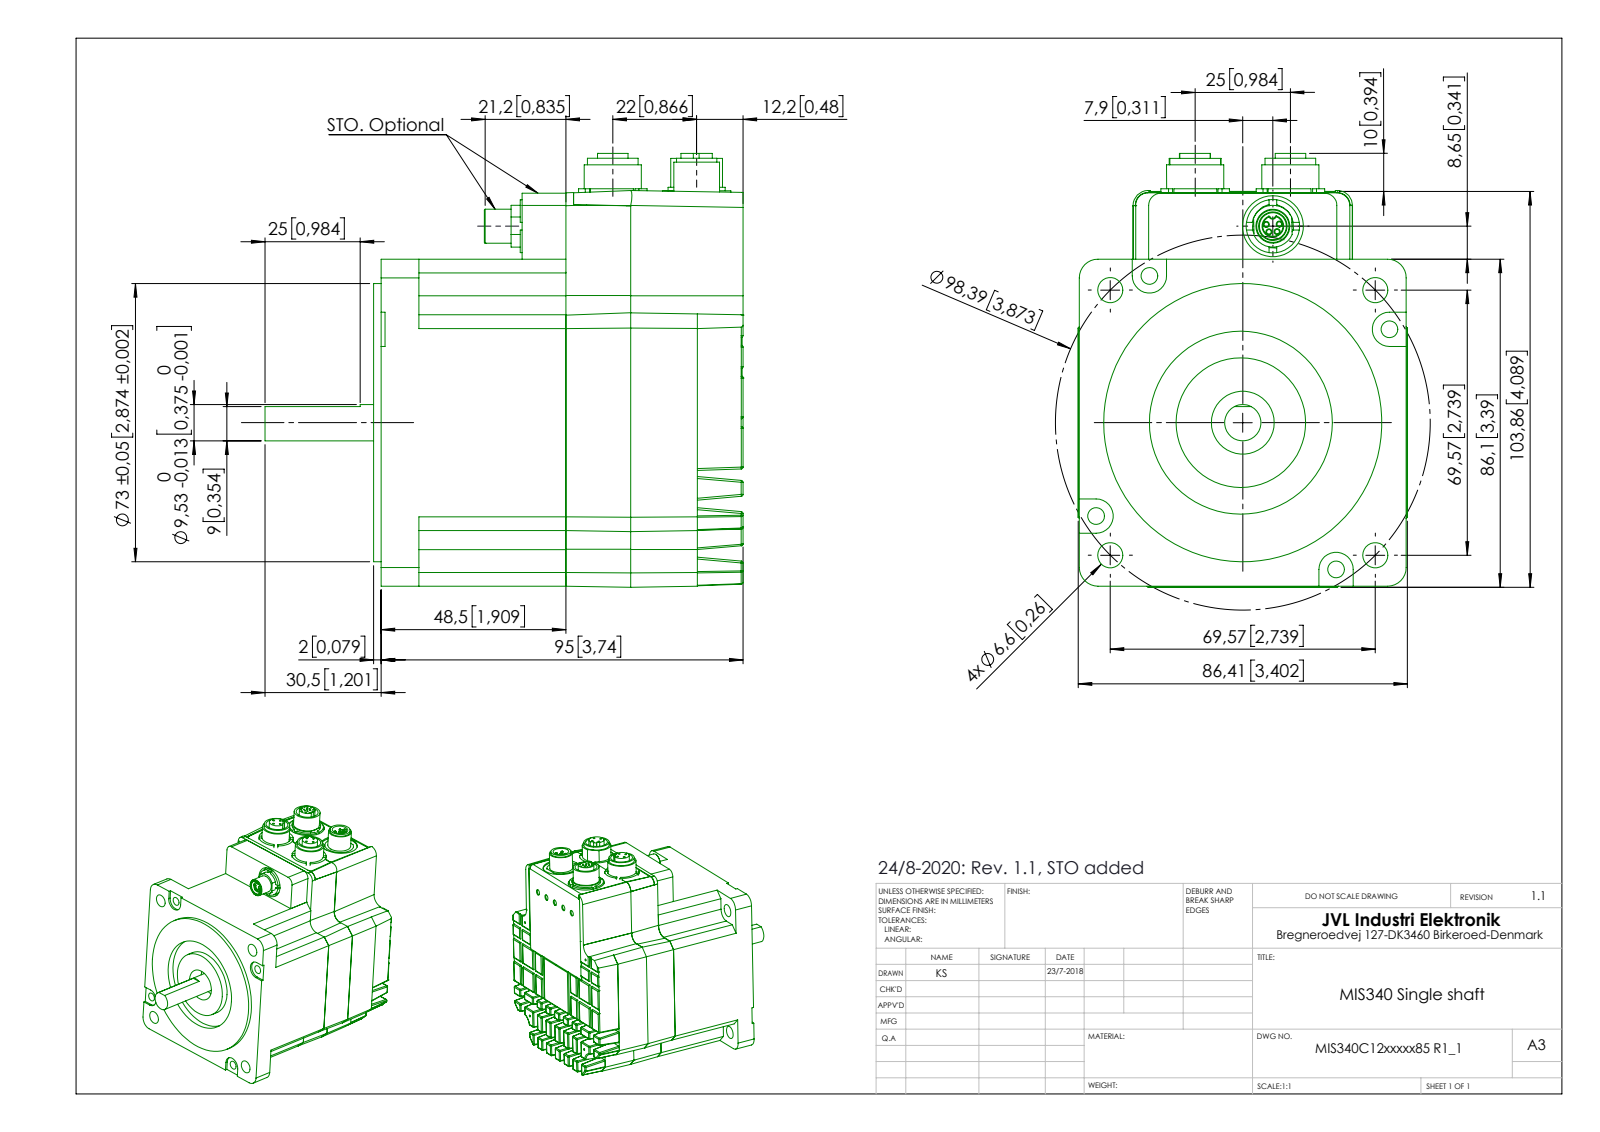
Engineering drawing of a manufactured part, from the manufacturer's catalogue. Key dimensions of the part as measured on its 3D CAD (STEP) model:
Part name (STEP PRODUCT): MIS340C12xxxxx85 R1_1
STEP written by: SolidWorks 2018 (AUTOMOTIVE_DESIGN)
Units: millimetres
Bodies: 2 solids, 1304 faces (539 planar, 573 cylindrical, 192 other)
Overall size (bounding box): 125.5 × 113.87 × 86.41
Volume: 665 007 mm³ · Surface area: 90 905 mm²
Round holes (diameter × count): ⌀0.7 ×17, ⌀1 ×12, ⌀3 ×5, ⌀1.2 ×4, ⌀4.3 ×4, ⌀4.4 ×4, ⌀6.6 ×4, ⌀11.5 ×3, ⌀16 ×2, ⌀19 ×2, ⌀7.1 ×1, ⌀8.2 ×1
Round bosses / shafts (diameter × count): ⌀1 ×5, ⌀18 ×3, ⌀15 ×3, ⌀8.2 ×3, ⌀13.3 ×2, ⌀8 ×2, ⌀73 ×1, ⌀34 ×1
Partial cylindrical surfaces — rounded edges, fillets, slot ends (radius × count): R0.5 ×164, R0.2 ×4, R4.5 ×4, R4.9 ×4, R5 ×4, R9.5 ×4, R0.48 ×3, R2 ×3
Main face-to-face distances: 85.8, 0.6, 50.5, 51.1, 2, 48.5, 49.1, 14.6, 97, 95
Hole centre spacings: 3.25, 3.54, 1.65, 2.48, 3.23, 3.26, 8.4, 25.04
